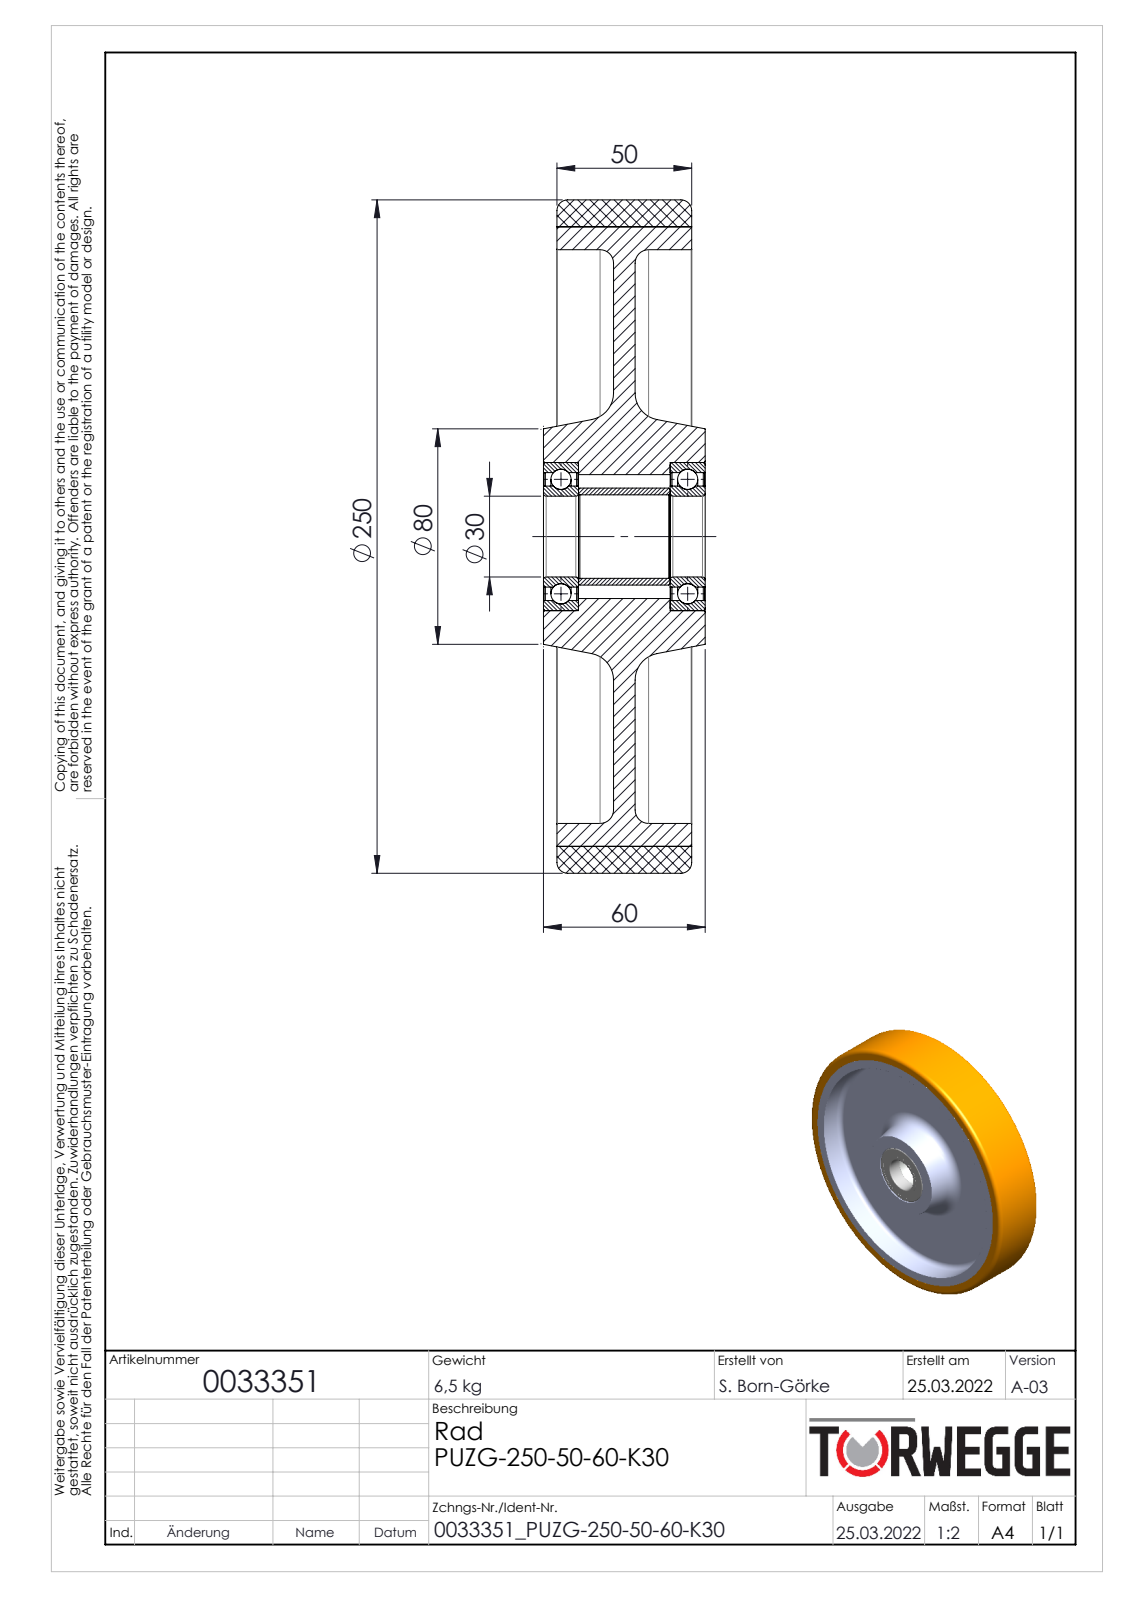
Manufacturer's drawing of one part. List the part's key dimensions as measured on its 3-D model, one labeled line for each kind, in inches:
Part name (STEP PRODUCT): 0033351
STEP written by: SolidWorks 2020 (AUTOMOTIVE_DESIGN)
Units: inches
Bodies: 13 solids, 160 faces (28 planar, 60 cylindrical, 72 other)
Overall size (bounding box): 9.843 × 9.843 × 2.362
Volume: 72.62 in³ · Surface area: 442.7 in²
Round holes (diameter × count): ⌀1.181 ×1, ⌀1.22 ×1, ⌀1.476 ×1, ⌀1.811 ×1, ⌀1.87 ×1, ⌀2.165 ×1, ⌀8.386 ×1, ⌀9.055 ×1
Round bosses / shafts (diameter × count): ⌀9.843 ×1, ⌀1.417 ×1
Main face-to-face distances: 0.315, 0.827, 1.142, 1.969, 1.339, 0.197, 1.024, 2.165, 0.512, 1.85
